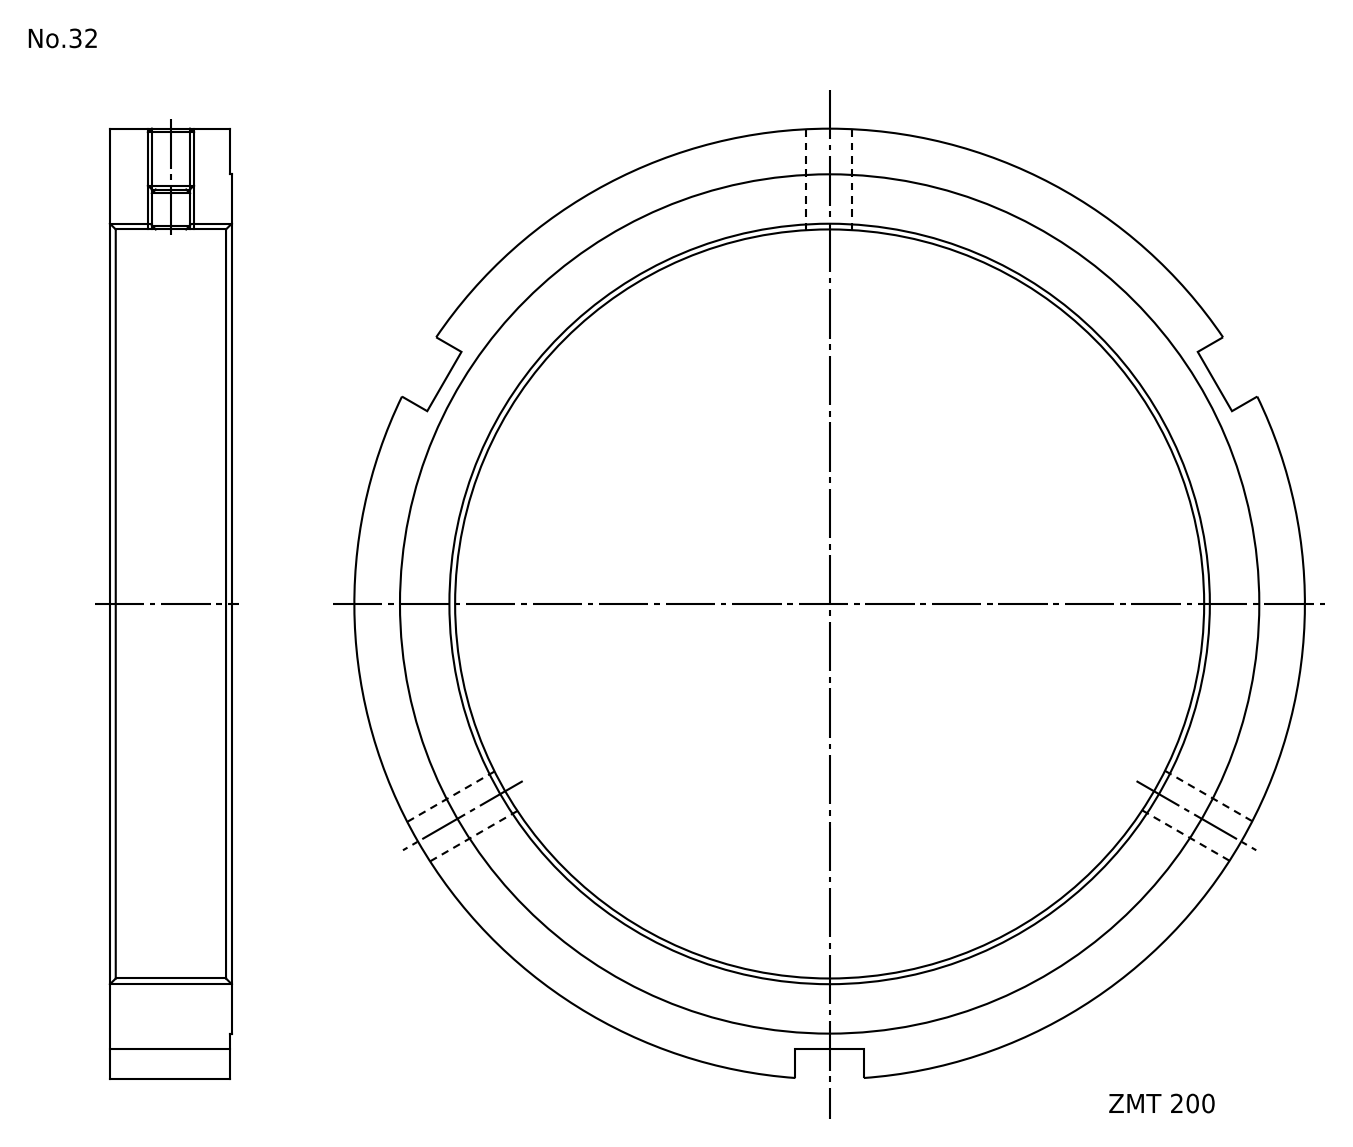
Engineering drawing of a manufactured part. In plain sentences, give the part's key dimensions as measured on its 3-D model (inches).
The part is named "FKD ZMT200". Its 3-D file was written by "Autodesk Inventor LT (CONFIG_CONTROL_DESIGN)". It is 1 solid with 20 faces: 12 planar, 8 cylindrical and 0 other. Overall it measures 9.843 by 9.83 by 1.26 inches. Its volume is 33.05 cubic inches and its surface area 128.7 square inches. Round holes: 3 of diameter 0.398, 1 of diameter 7.874. Round bosses or shafts: 1 of diameter 9.843, 1 of diameter 8.898. The main face-to-face distances are 1.26, 0.02, 1.24, 0.709.
